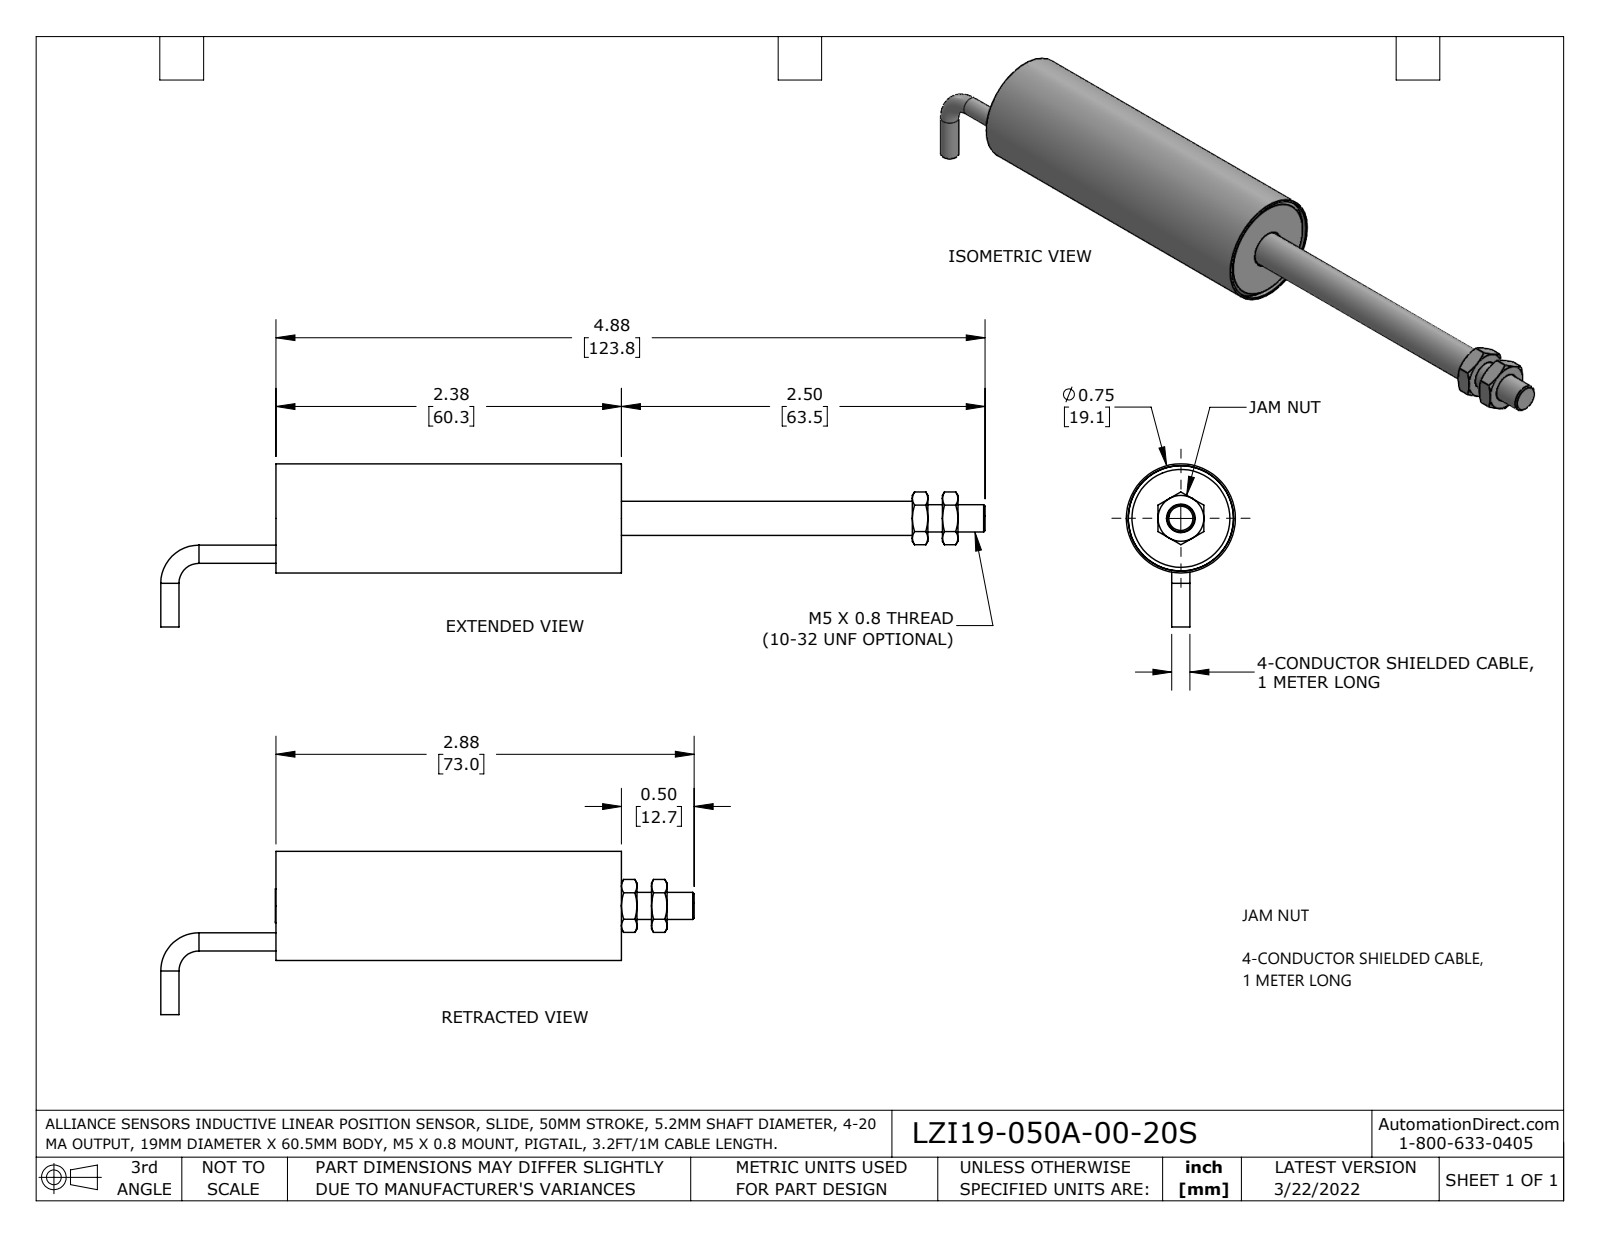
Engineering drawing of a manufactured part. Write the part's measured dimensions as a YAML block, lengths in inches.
part_name: "3100-0076_B18.2.4.5M - Hex jam nut, M5 x 0.8 --D-N; 3120-0006-06_-02-0Y; 3120-0007-ZY; 3300-0008-06_-02 (+6 more)"
step_written_by: "SolidWorks 2021 (AUTOMOTIVE_DESIGN)"
units: inches
bodies: {solids: 10, faces: 137, planar: 42, cylindrical: 44, other: 51}
overall_size: [5.668, 1.121, 0.75]
volume: 0.439
surface_area: 23.47
round_holes:
  - {diameter: 0.165, count: 1}
  - {diameter: 0.188, count: 1}
  - {diameter: 0.197, count: 1}
  - {diameter: 0.234, count: 1}
  - {diameter: 0.281, count: 1}
  - {diameter: 0.68, count: 1}
  - {diameter: 0.725, count: 1}
round_bosses_or_shafts:
  - {diameter: 0.125, count: 2}
  - {diameter: 0.75, count: 1}
  - {diameter: 0.723, count: 1}
  - {diameter: 0.278, count: 1}
  - {diameter: 0.187, count: 1}
partial_cylinders:
  - {radius: 0.052, count: 1}
face_to_face_distances: [0.06, 2.295, 0.08, 2.235, 2.355, 0.315, 0.206, 0.106, 0.374, 0.03]
